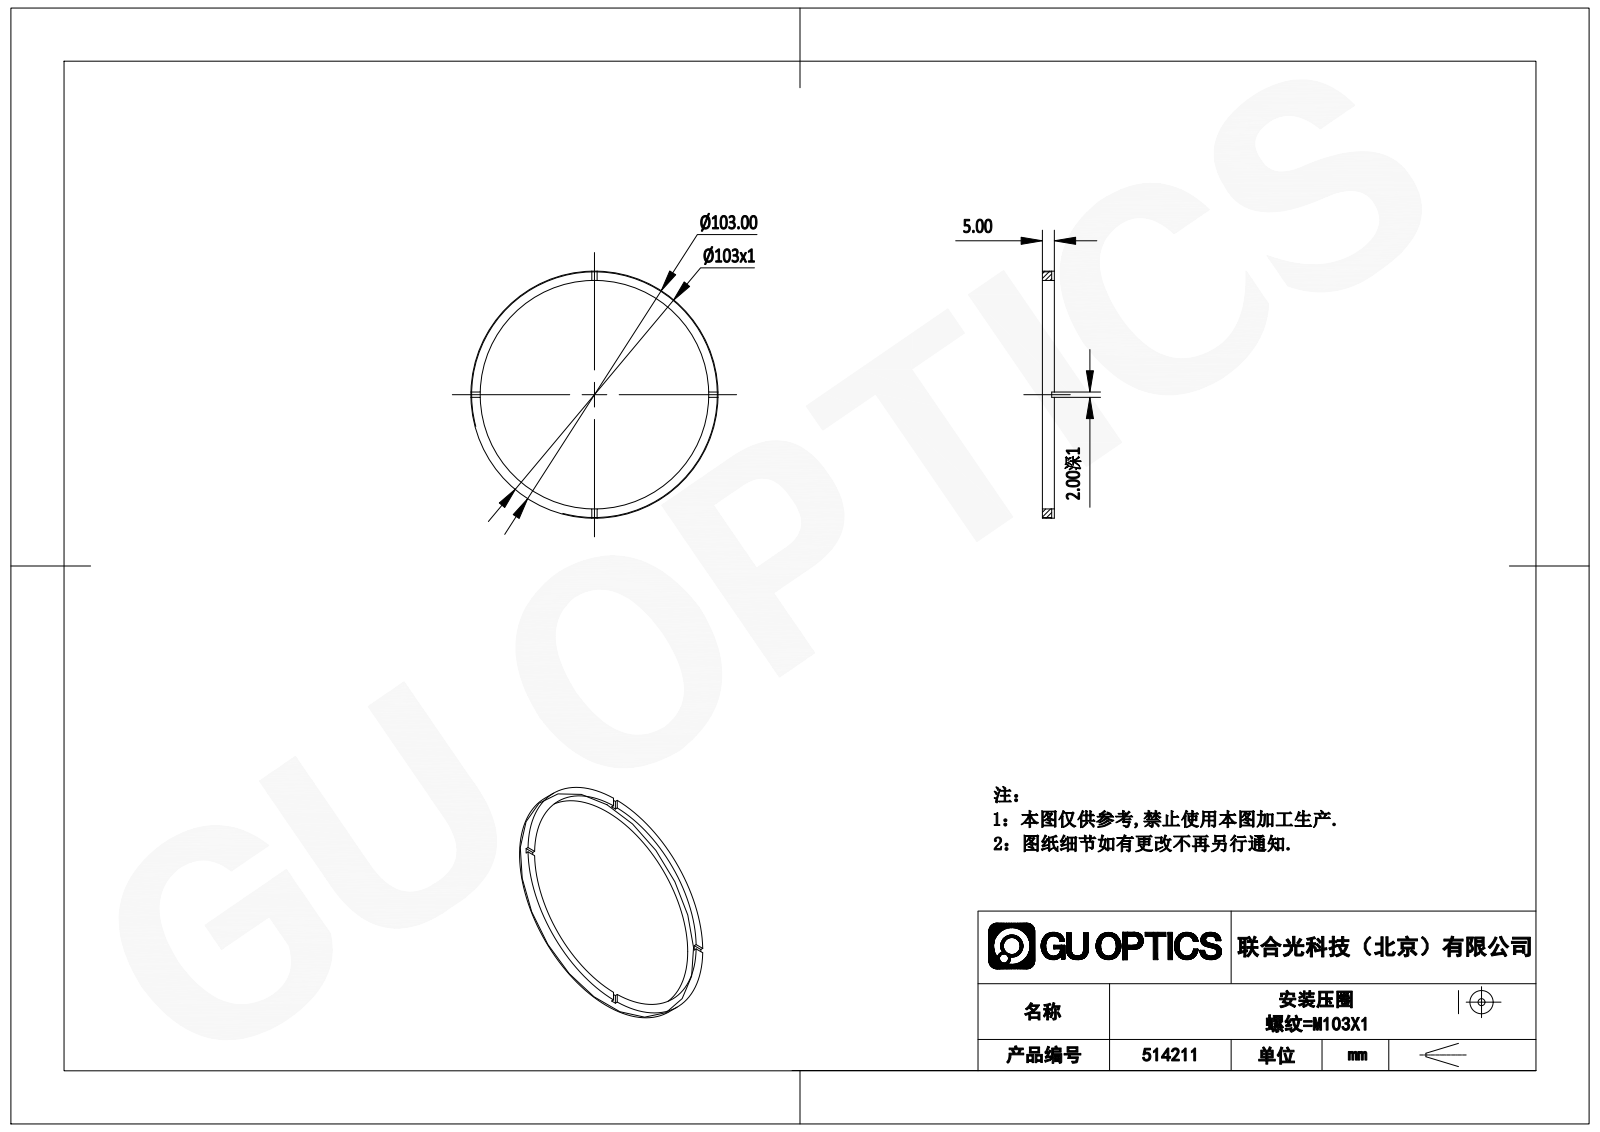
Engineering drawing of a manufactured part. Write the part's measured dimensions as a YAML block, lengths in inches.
part_name: "514211"
step_written_by: "SolidWorks 2020 (CONFIG_CONTROL_DESIGN)"
units: inches
bodies: {solids: 1, faces: 21, planar: 17, cylindrical: 4, other: 0}
overall_size: [4.055, 4.055, 0.197]
volume: 0.378
surface_area: 8.702
round_holes:
  - {diameter: 3.74, count: 1}
round_bosses_or_shafts:
  - {diameter: 4.055, count: 1}
face_to_face_distances: [0.197, 0.157, 0.039, 0.079]
